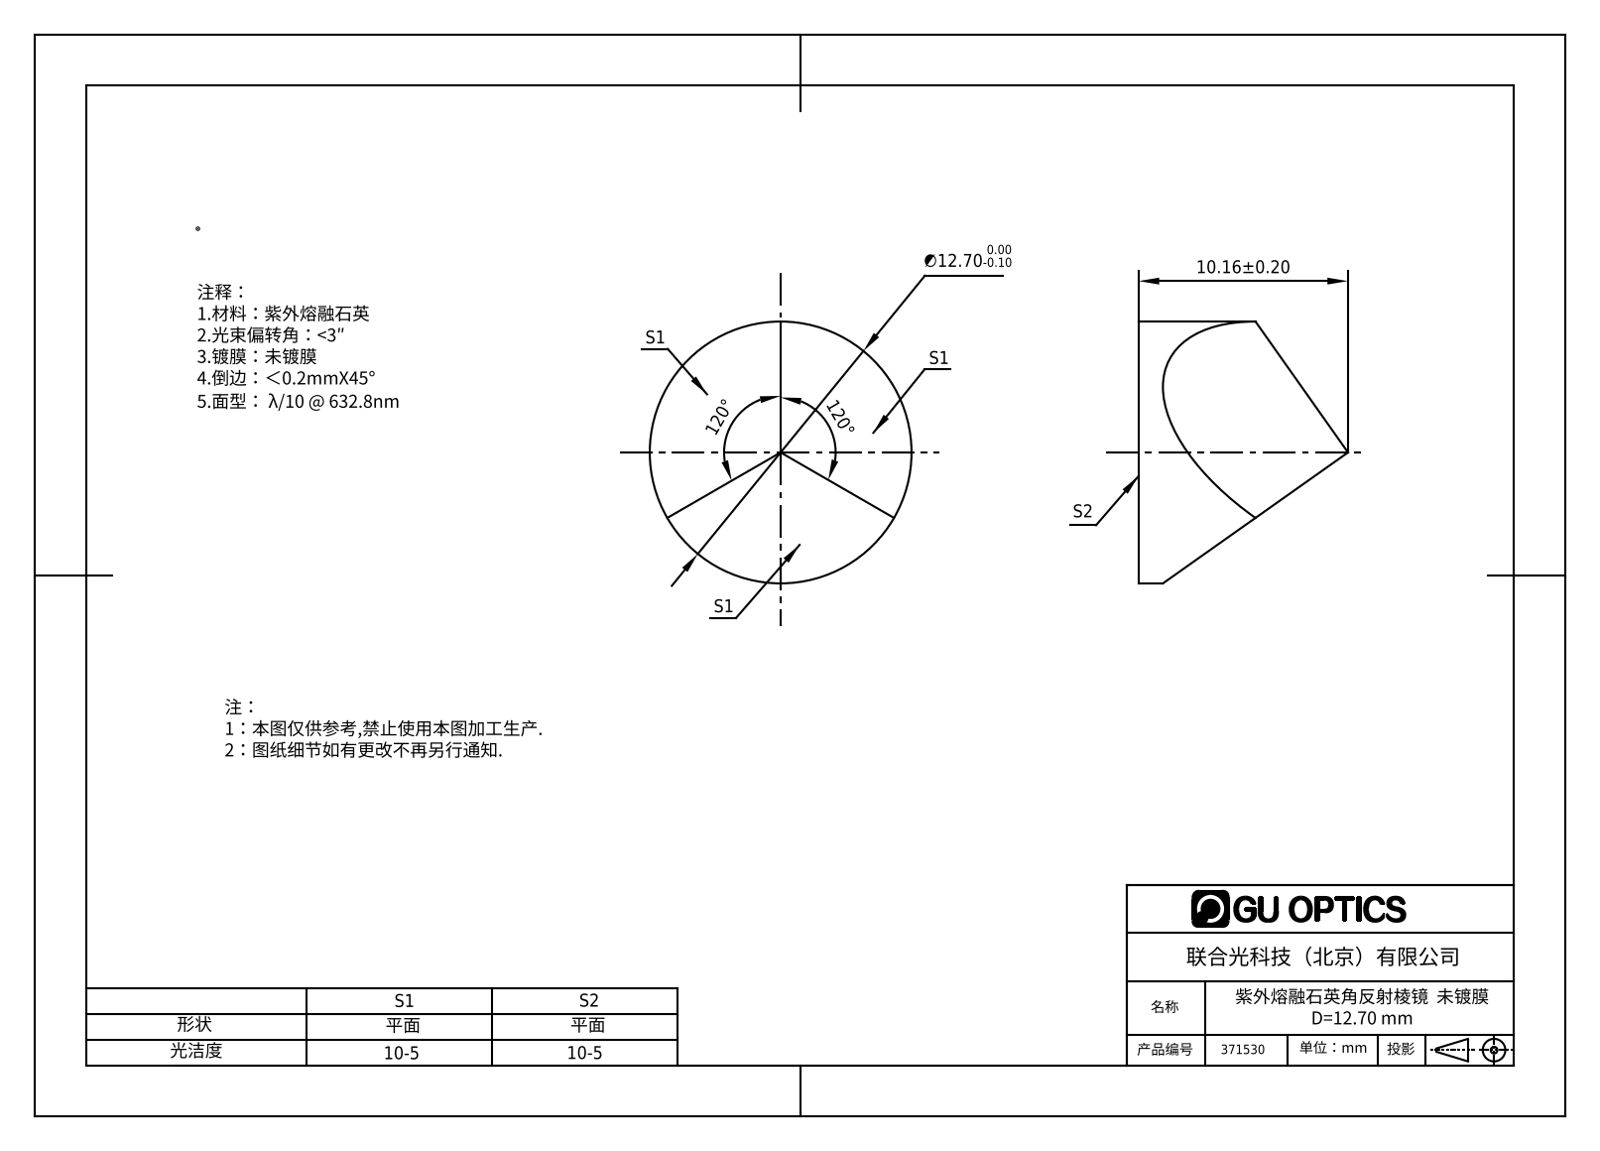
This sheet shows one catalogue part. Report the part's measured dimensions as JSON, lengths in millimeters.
{"part_name": "371530", "step_written_by": "SolidWorks 2016 (CONFIG_CONTROL_DESIGN)", "units": "millimeters", "bodies": {"solids": 1, "faces": 6, "planar": 4, "cylindrical": 2, "other": 0}, "overall_size": [12.7, 12.7, 10.16], "volume_mm3": 660, "surface_area_mm2": 455, "round_bosses_or_shafts": [[12.7, 1]]}
